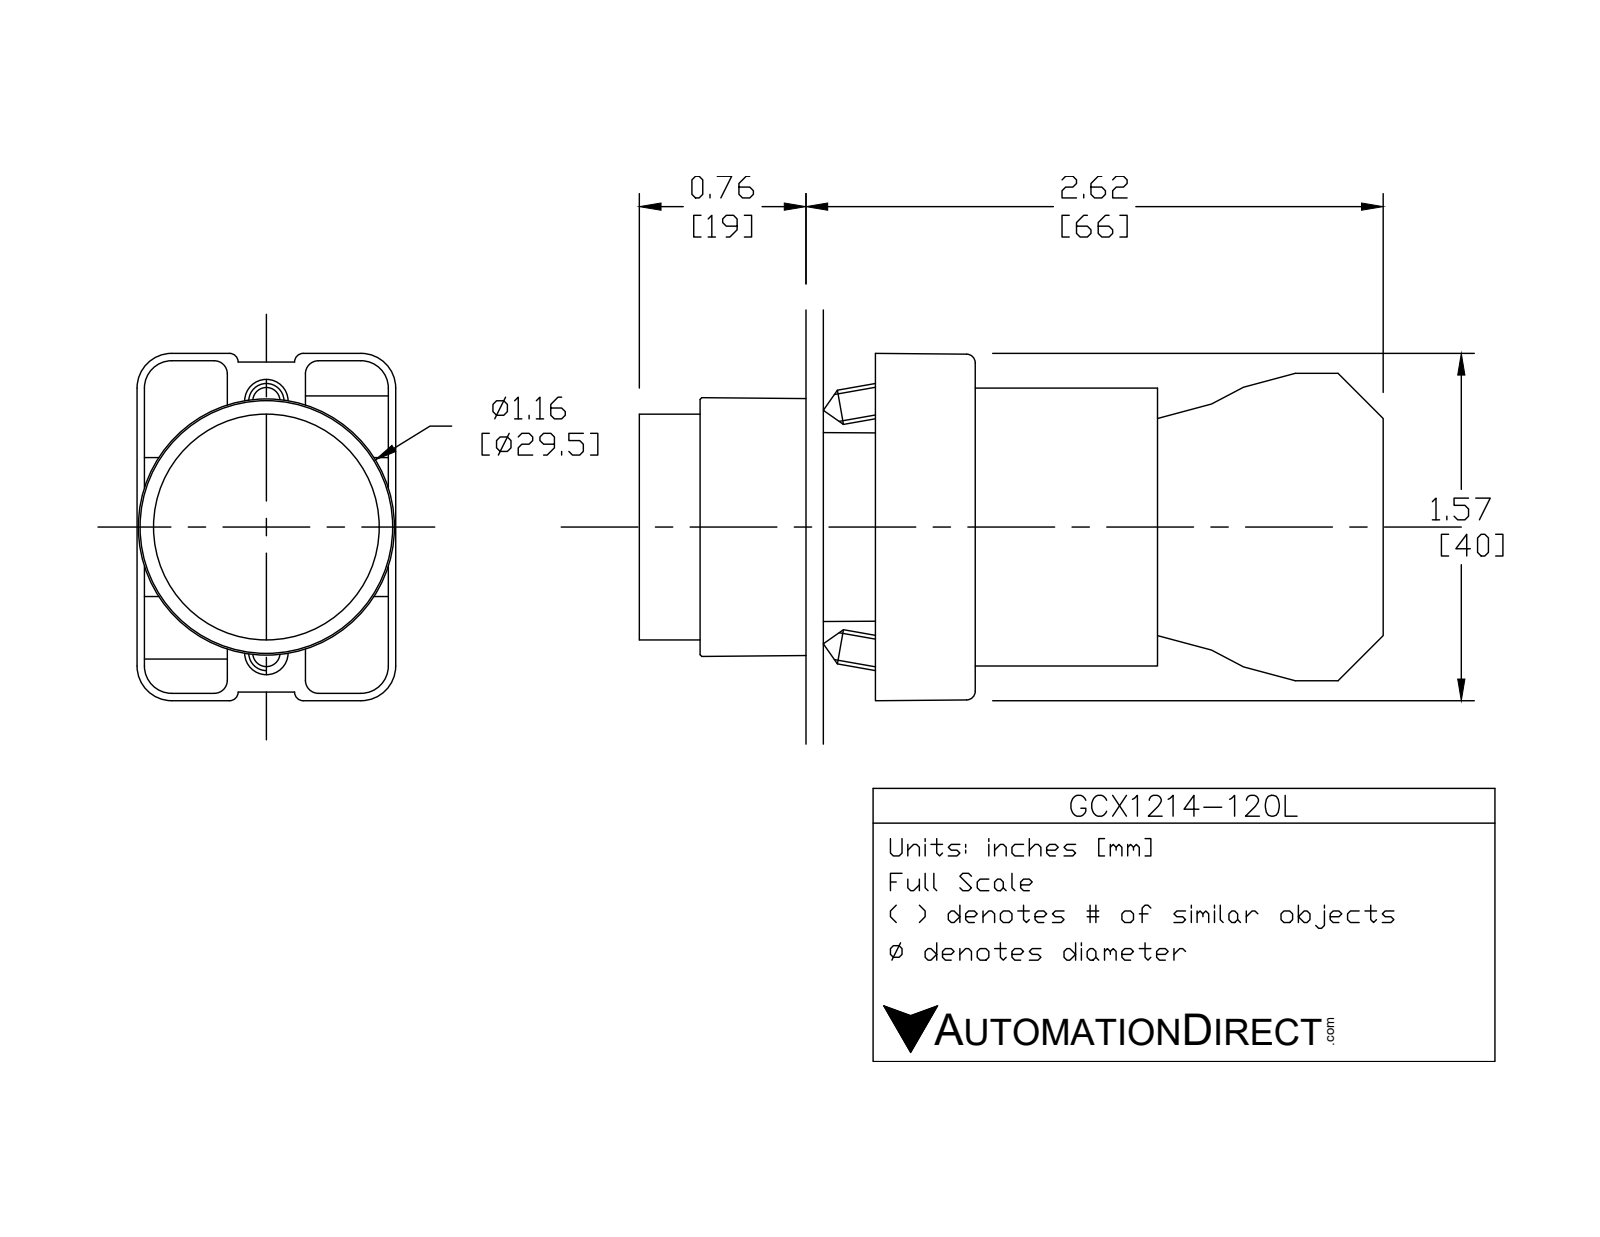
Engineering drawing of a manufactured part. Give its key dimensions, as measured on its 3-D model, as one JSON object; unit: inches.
{"part_name": "ecx1029; GCX1214L OPERATOR; ecx1040; GCX1214-120L (+1 more)", "step_written_by": "SolidWorks 2016 (AUTOMOTIVE_DESIGN)", "units": "inches", "bodies": {"solids": 7, "faces": 425, "planar": 250, "cylindrical": 144, "other": 31}, "overall_size": [3.319, 1.581, 1.177], "volume_in3": 2.721, "surface_area_in2": 36.32, "round_holes": [[0.079, 2], [0.124, 2], [0.13, 2], [0.087, 1], [0.197, 1], [0.469, 1], [0.878, 1], [0.888, 1], [1.024, 1]], "round_bosses_or_shafts": [[0.157, 4], [1.175, 1], [1.004, 1], [0.945, 1], [0.856, 1], [0.78, 1], [0.504, 1]], "partial_cylinders_radius": [[0.059, 24], [0.041, 12], [0.124, 12], [0.157, 12], [0.039, 8], [0.128, 2], [0.02, 1], [0.063, 1]], "face_to_face_distances": [0.827, 0.579, 1.171, 2.02, 1.193, 0.031, 0.033, 0.573, 1.165, 0.593], "hole_center_spacings": [0.236, 0.544, 0.472, 0.49]}
